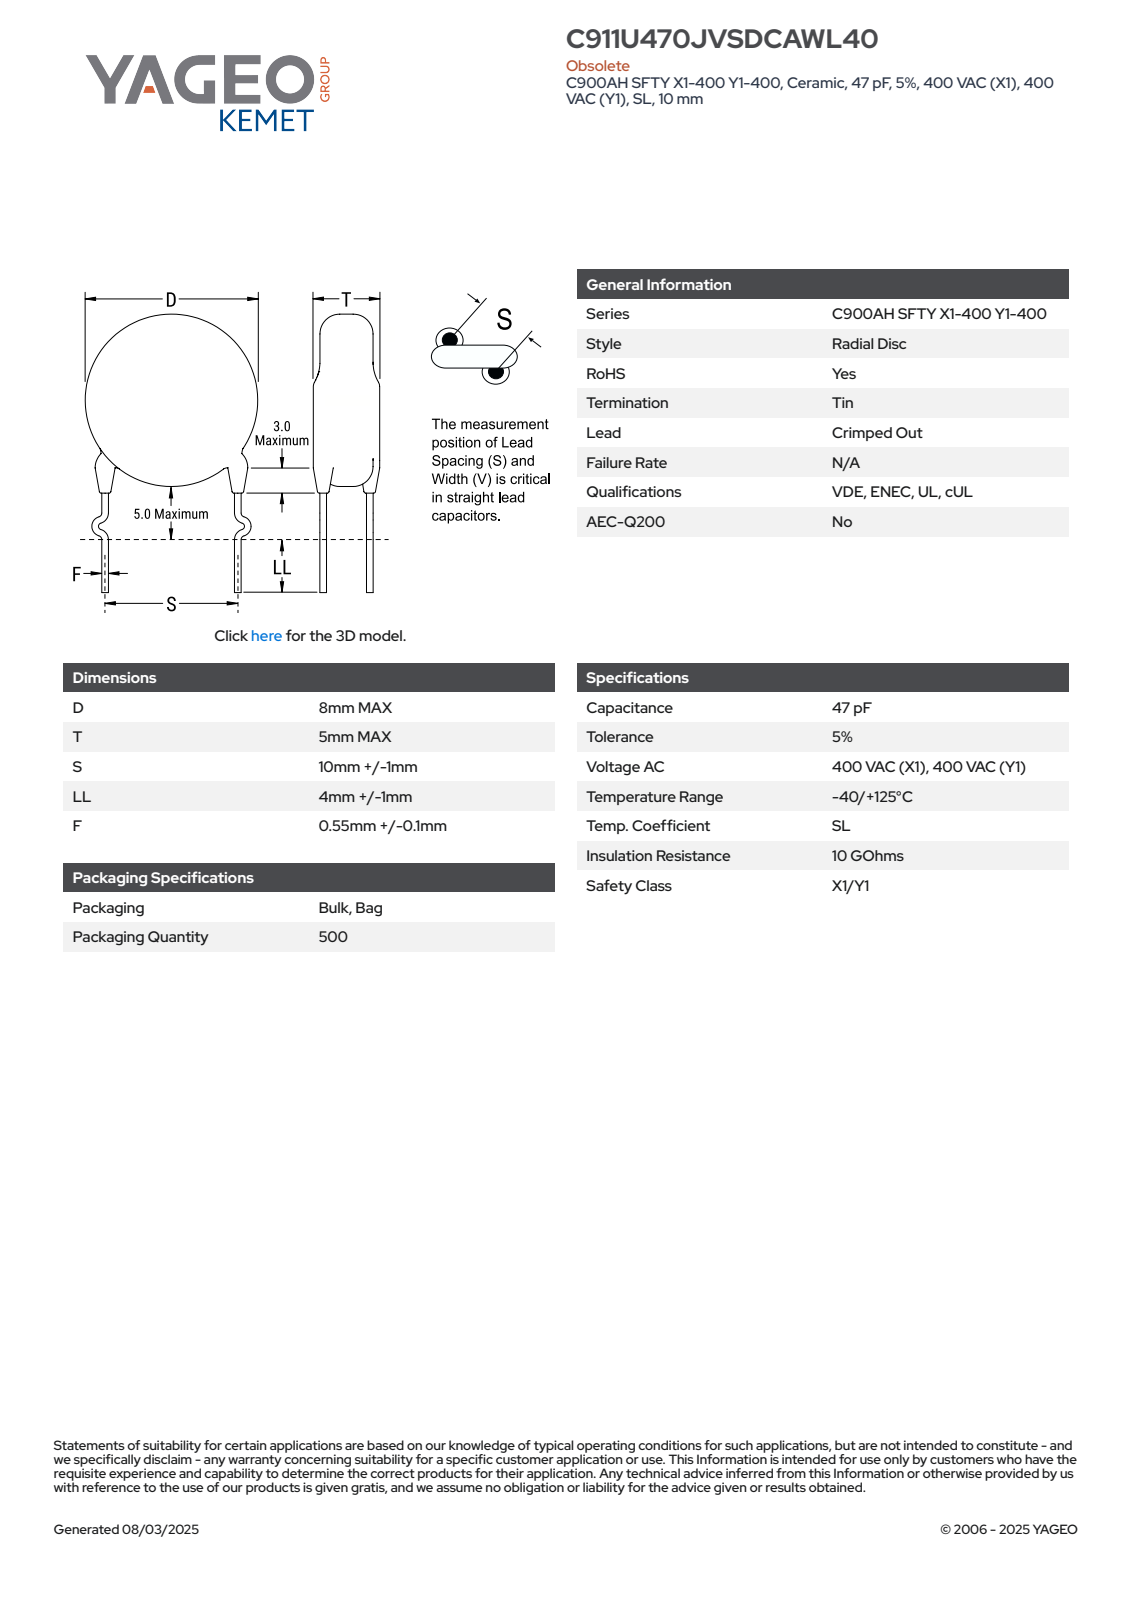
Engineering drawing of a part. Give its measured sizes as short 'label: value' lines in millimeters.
name: CCD_KCOC900_D8T5S10LL5F0.55
written by: SolidWorks 2014 (AUTOMOTIVE_DESIGN)
unit: mm
bodies: 4 solids, 93 faces (63 planar, 10 cylindrical, 20 other)
size: 18 × 14.24 × 6.32
volume: 257 mm³; area: 283 mm²
bosses: 4× ⌀1.2, 1× ⌀8
face distances: 5, 0.83, 4.42, 3.59, 3.39, 0.52, 0.31, 0.67, 1.71, 2.46
